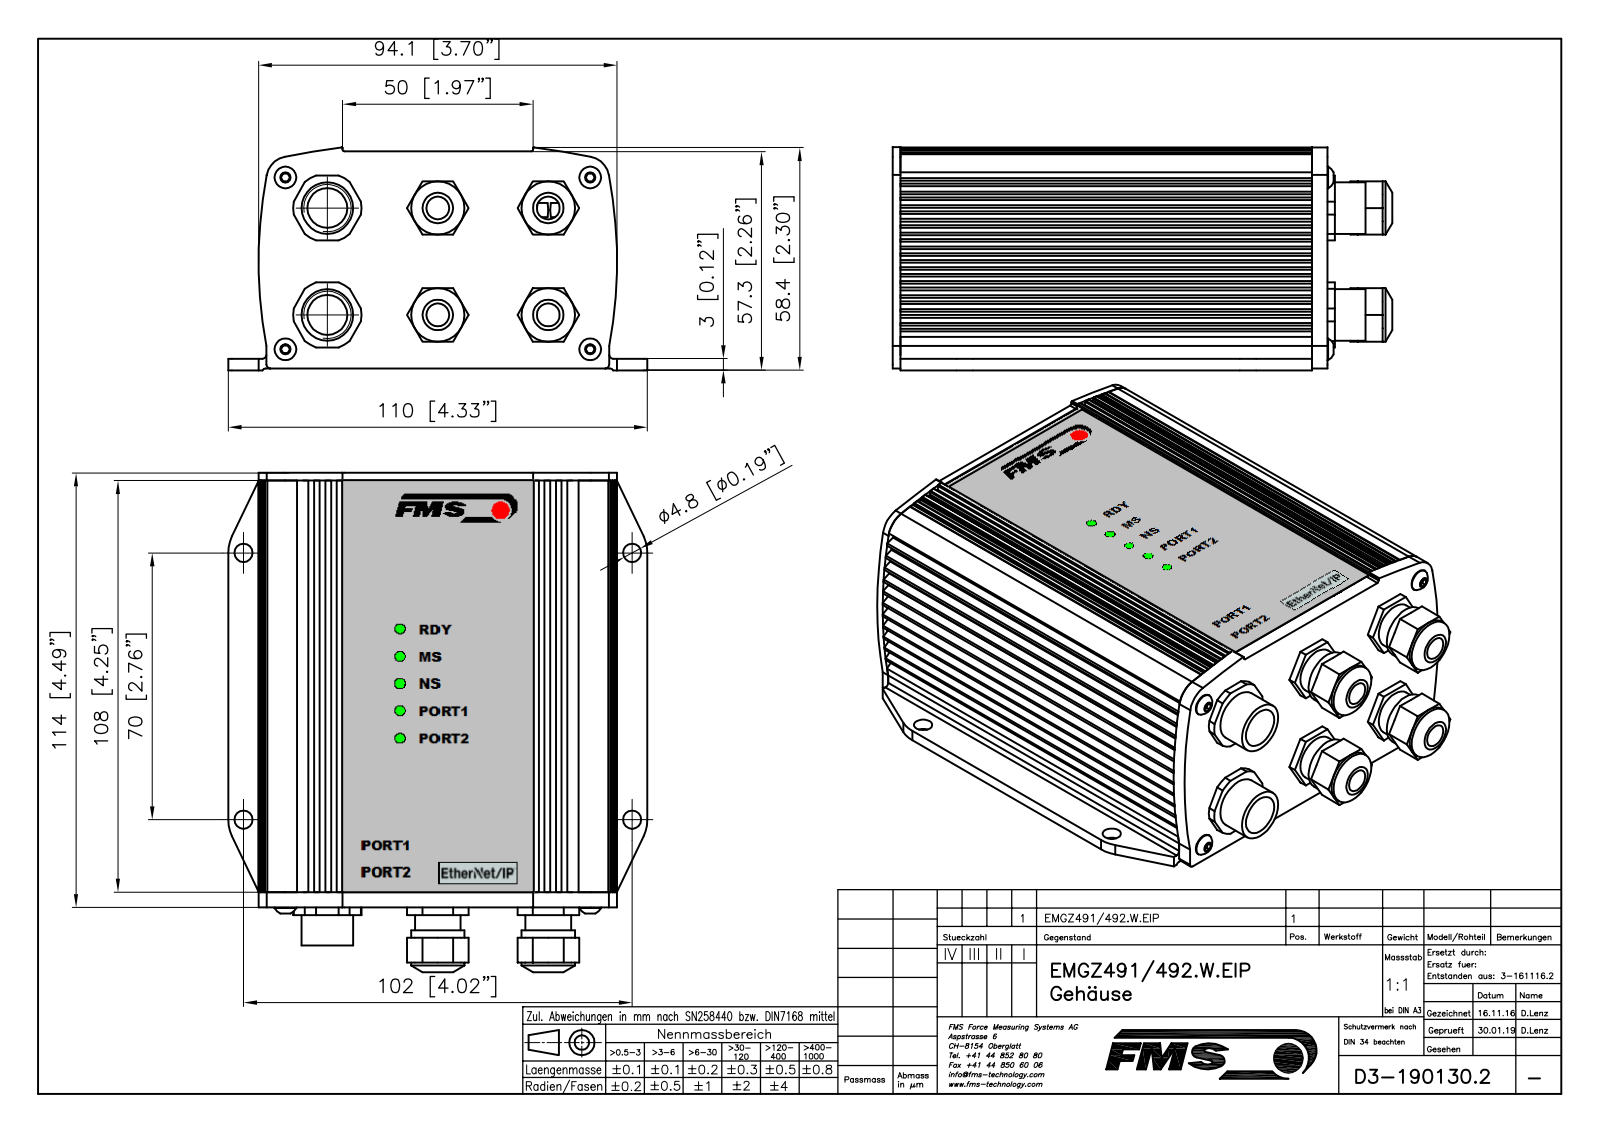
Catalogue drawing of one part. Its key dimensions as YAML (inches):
part_name: "E1901302_STP; E1609204; EINPRESSGEWINDEBOLZEN_M4X10; E1105119 (+7 more)"
step_written_by: "Mechanical Desktop 2009 (CONFIG_CONTROL_DESIGN)"
units: inches
bodies: {solids: 18, faces: 812, planar: 403, cylindrical: 328, other: 81}
overall_size: [5.157, 4.331, 2.299]
volume: 8.581
surface_area: 170.5
round_holes:
  - {diameter: 0.102, count: 5}
  - {diameter: 0.126, count: 4}
  - {diameter: 0.189, count: 4}
  - {diameter: 0.236, count: 4}
  - {diameter: 0.42, count: 4}
  - {diameter: 0.411, count: 2}
  - {diameter: 0.512, count: 2}
  - {diameter: 0.578, count: 2}
  - {diameter: 0.157, count: 1}
round_bosses_or_shafts:
  - {diameter: 0.551, count: 4}
  - {diameter: 0.472, count: 4}
  - {diameter: 0.236, count: 4}
  - {diameter: 0.224, count: 4}
  - {diameter: 0.118, count: 4}
  - {diameter: 0.087, count: 4}
  - {diameter: 0.63, count: 2}
  - {diameter: 0.531, count: 2}
partial_cylinders:
  - {radius: 0.01, count: 70}
  - {radius: 0.079, count: 12}
  - {radius: 0.039, count: 6}
  - {radius: 0.394, count: 4}
  - {radius: 0.008, count: 2}
  - {radius: 0.02, count: 2}
  - {radius: 0.197, count: 2}
  - {radius: 0.236, count: 2}
face_to_face_distances: [0.079, 2.146, 2.067, 0.157, 2.224, 4.252, 4.488, 4.331, 4.409, 0.098]
hole_center_spacings: [1.142, 1.587, 1.102, 0.535, 0.559, 1.482, 1.52, 1.606]
